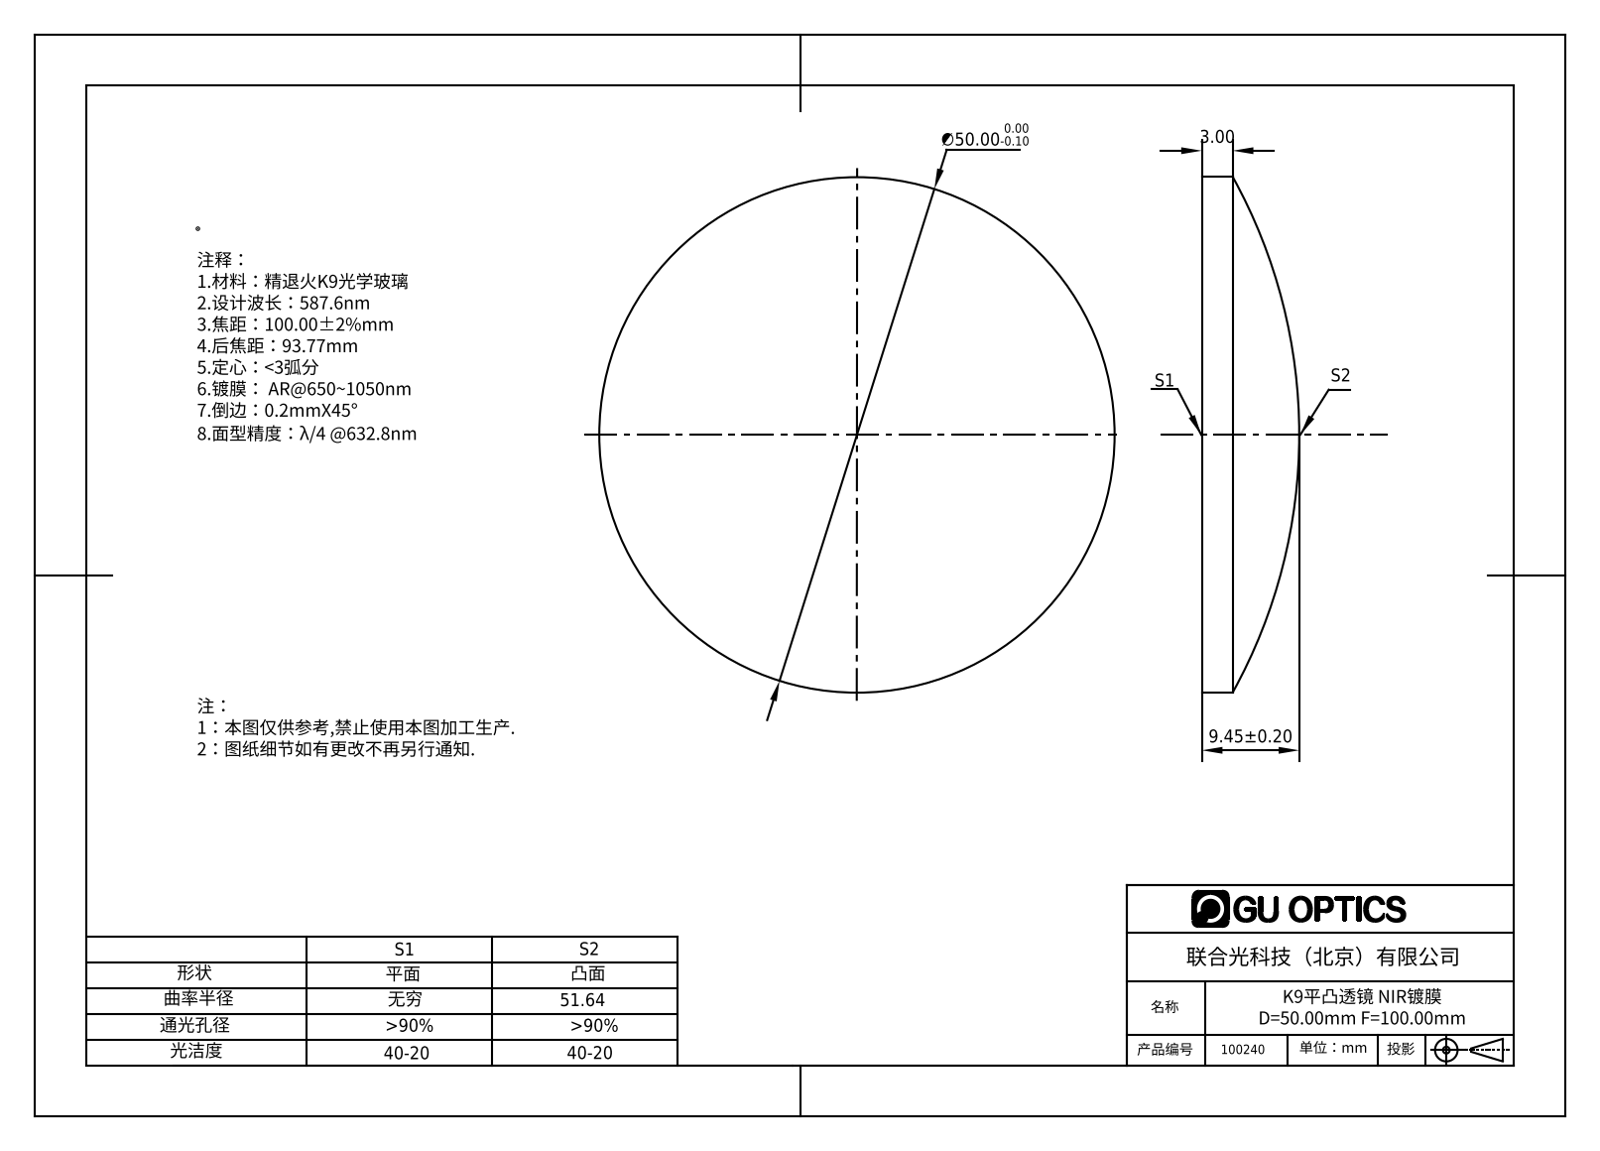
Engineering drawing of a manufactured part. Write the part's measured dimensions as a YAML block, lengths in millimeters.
part_name: "100240"
step_written_by: "SolidWorks 2016 (AUTOMOTIVE_DESIGN)"
units: millimeters
bodies: {solids: 1, faces: 5, planar: 1, cylindrical: 2, other: 2}
overall_size: [50, 50, 9.45]
volume: 12363
surface_area: 4529
round_bosses_or_shafts:
  - {diameter: 50, count: 1}
